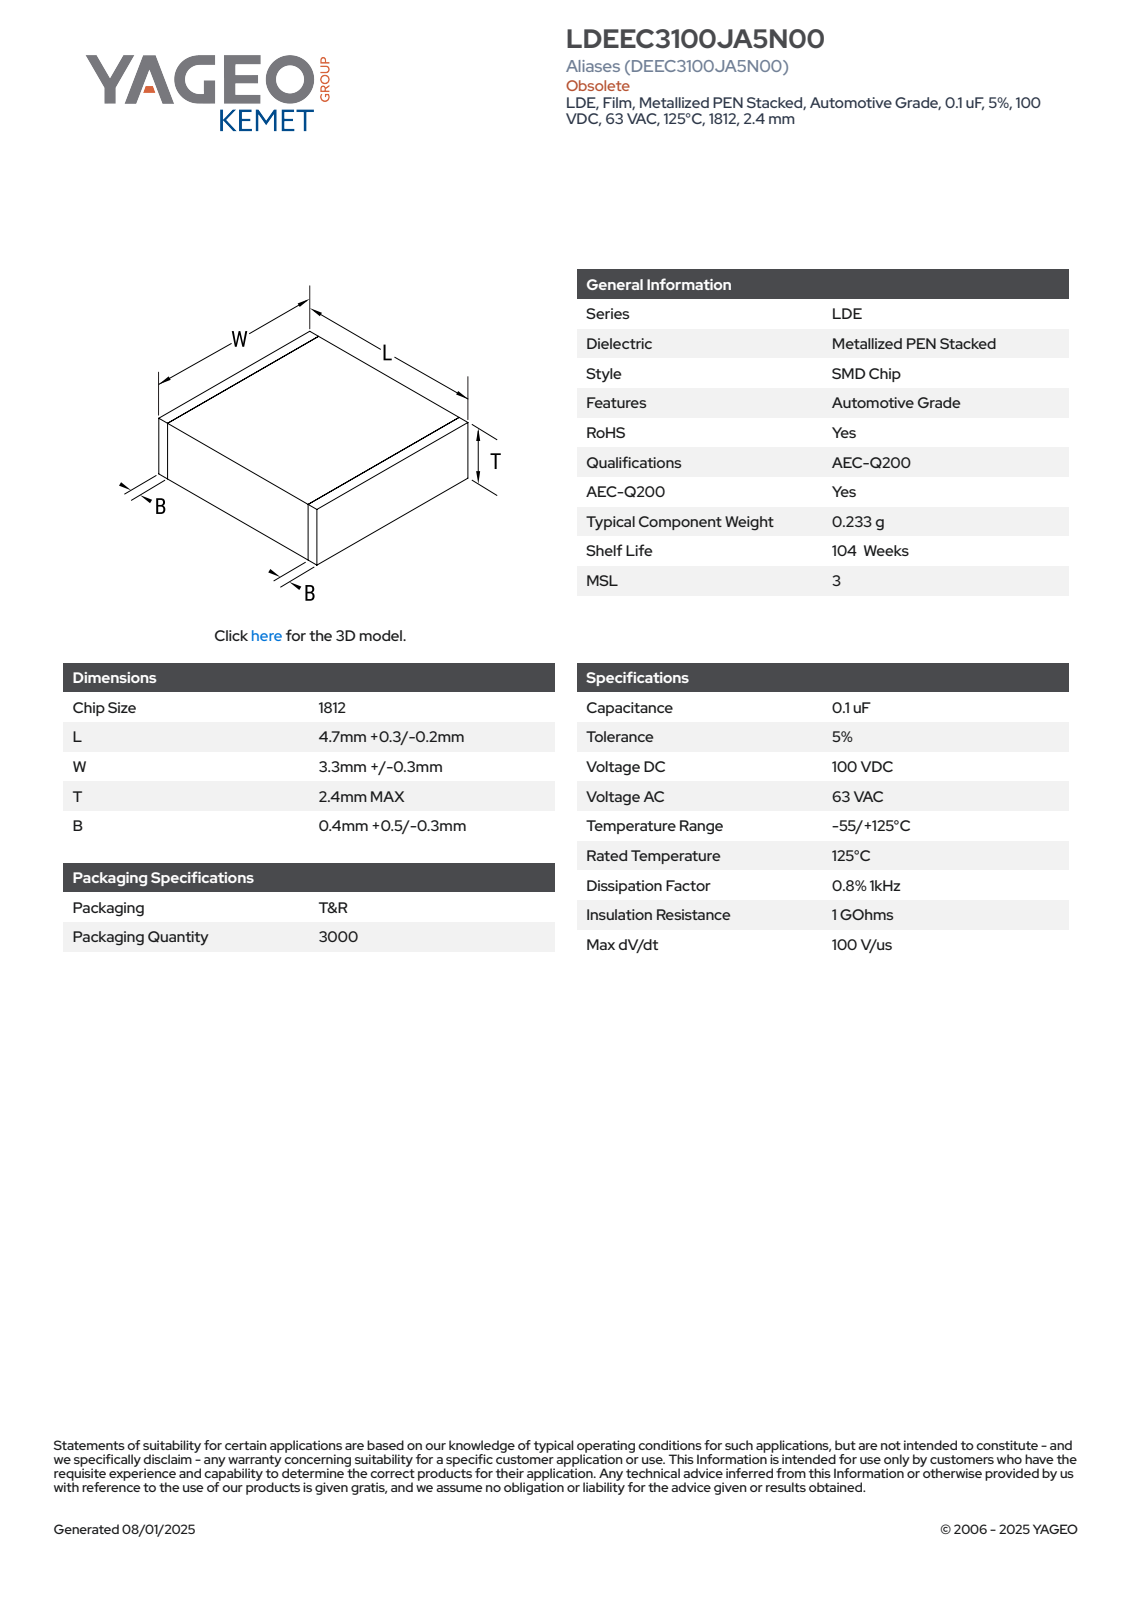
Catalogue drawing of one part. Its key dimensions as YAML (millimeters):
part_name: "CFS_LDELDB_1812_L5W3.6T2.4B0.9"
step_written_by: "SolidWorks 2020 (AUTOMOTIVE_DESIGN)"
units: millimeters
bodies: {solids: 4, faces: 73, planar: 73, cylindrical: 0, other: 0}
overall_size: [5, 3.6, 2.4]
volume: 43
surface_area: 78
face_to_face_distances: [2.38, 3.58, 5, 2.39, 3.59, 2.4, 3.6, 0.5, 4.5, 4]
